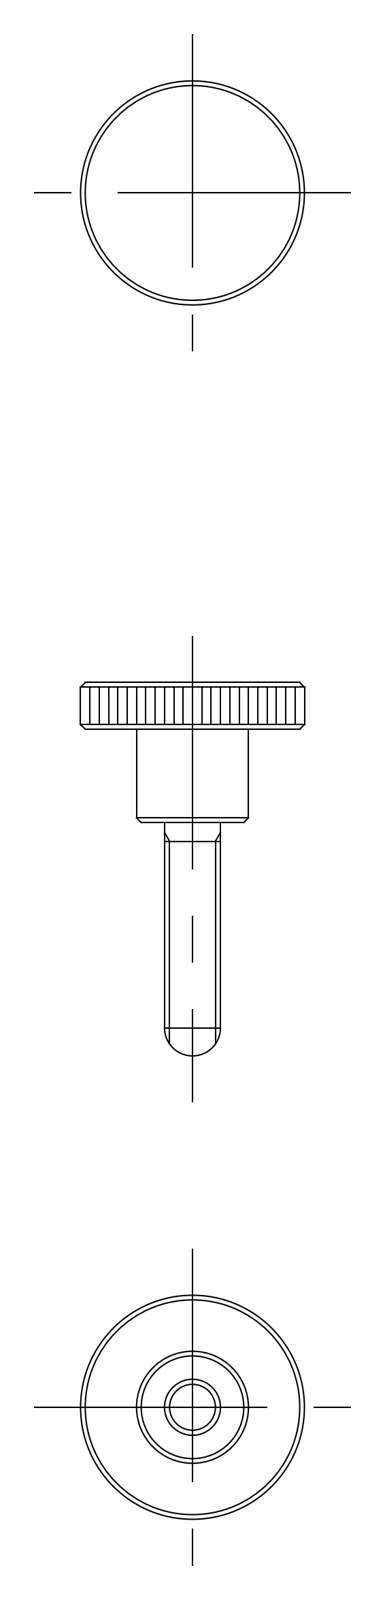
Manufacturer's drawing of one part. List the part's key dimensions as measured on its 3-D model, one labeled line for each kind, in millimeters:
Part name (STEP PRODUCT): knob
STEP written by: CADfix (AUTOMOTIVE_DESIGN)
Units: millimetres
Bodies: 1 solid, 16 faces (0 planar, 0 cylindrical, 16 other)
Overall size (bounding box): 40 × 24 × 24
Volume: 4 055 mm³ · Surface area: 2 046 mm²
